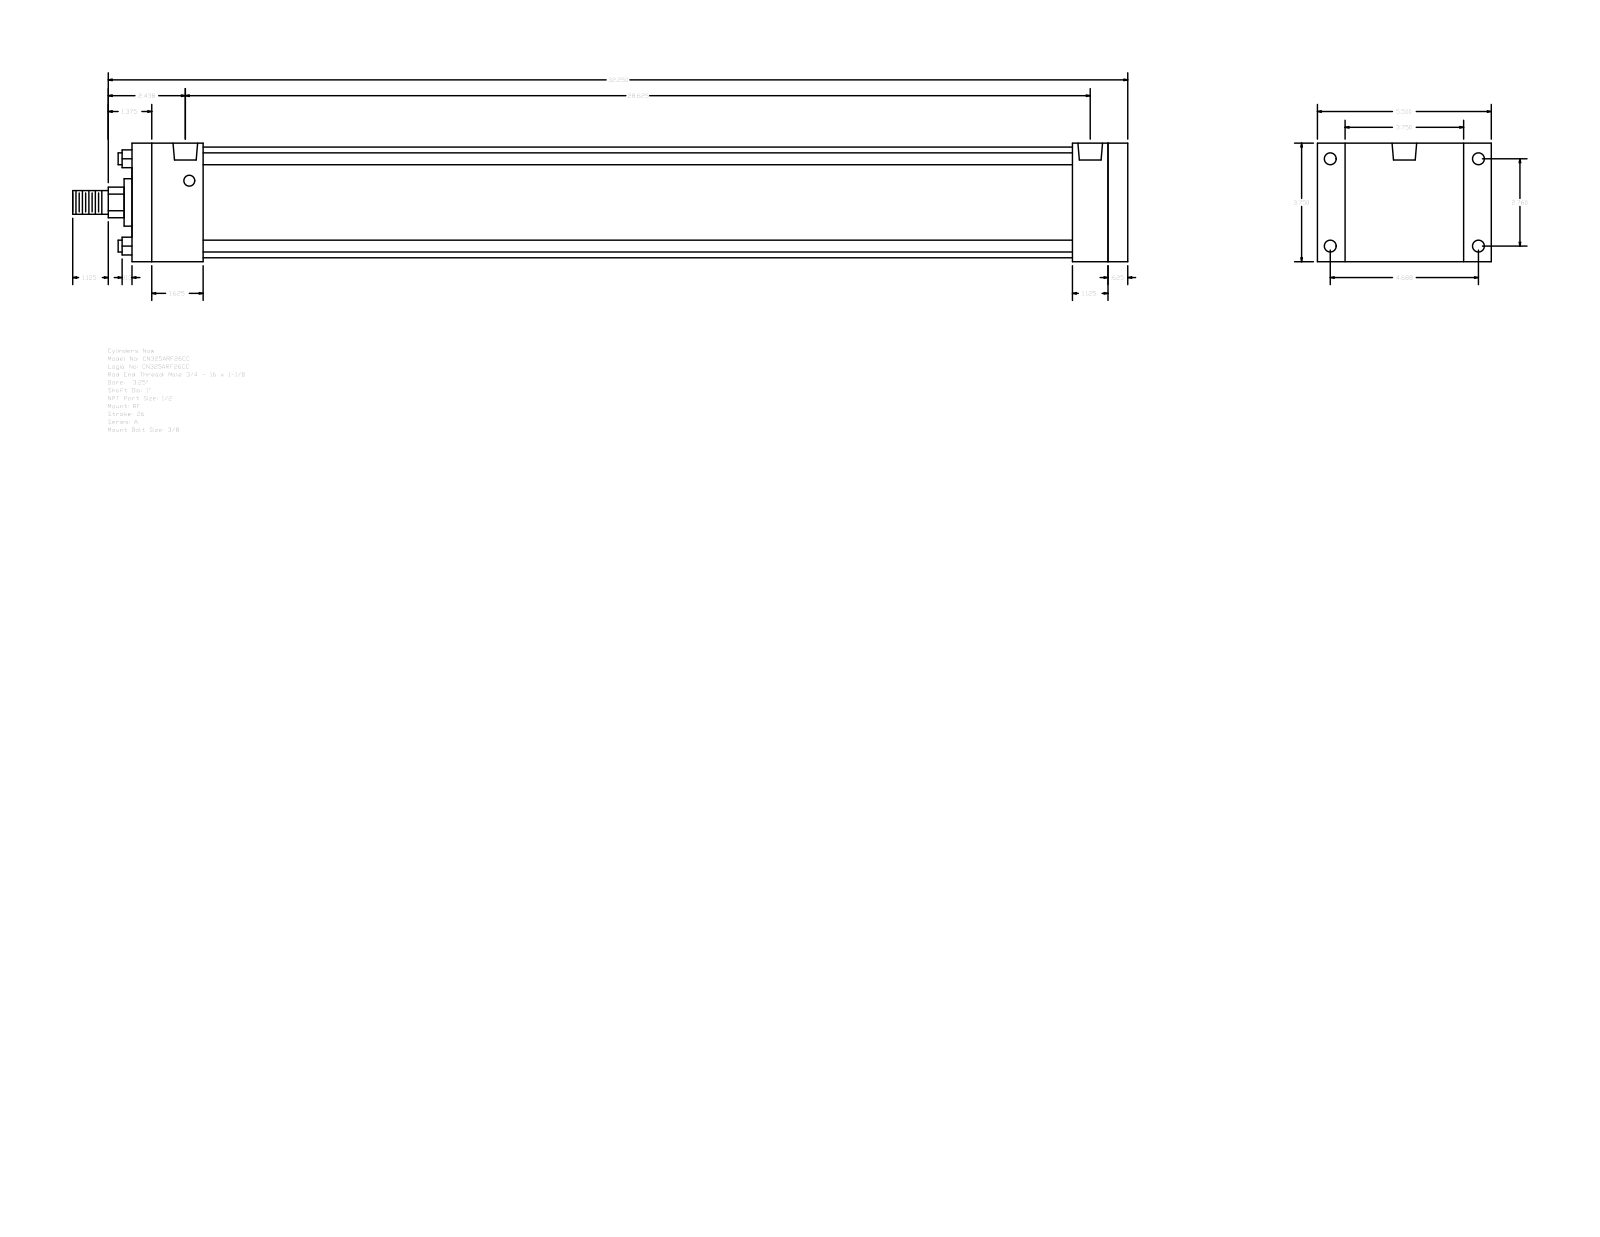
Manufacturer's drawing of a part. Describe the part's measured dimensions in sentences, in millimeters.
The part is named "A_RF__0325_1". Its 3-D file was written by "GSSL Pune (CONFIG_CONTROL_DESIGN)". It is 0 solids with 92 faces: 64 planar, 28 cylindrical and 0 other. Overall it measures 847.73 by 139.7 by 95.25 millimeters. Round holes: 4 of diameter 8.73, 4 of diameter 9.53, 2 of diameter 19.77. Round bosses or shafts: 4 of diameter 9.53, 1 of diameter 88.9, 1 of diameter 38.1, 1 of diameter 25.4, 1 of diameter 19.05. Partial cylindrical surfaces (rounded edges, fillets, slot ends): 1 of radius 12.29. The main face-to-face distances are 95.24, 800.1, 784.22, 15.88, 22.23, 117.47, 28.57, 755.65, 44.45, 57.15. The hole center spacings are 3.18, 70.1, 119.06, 138.16, 720.72, 723.9, 727.08.
